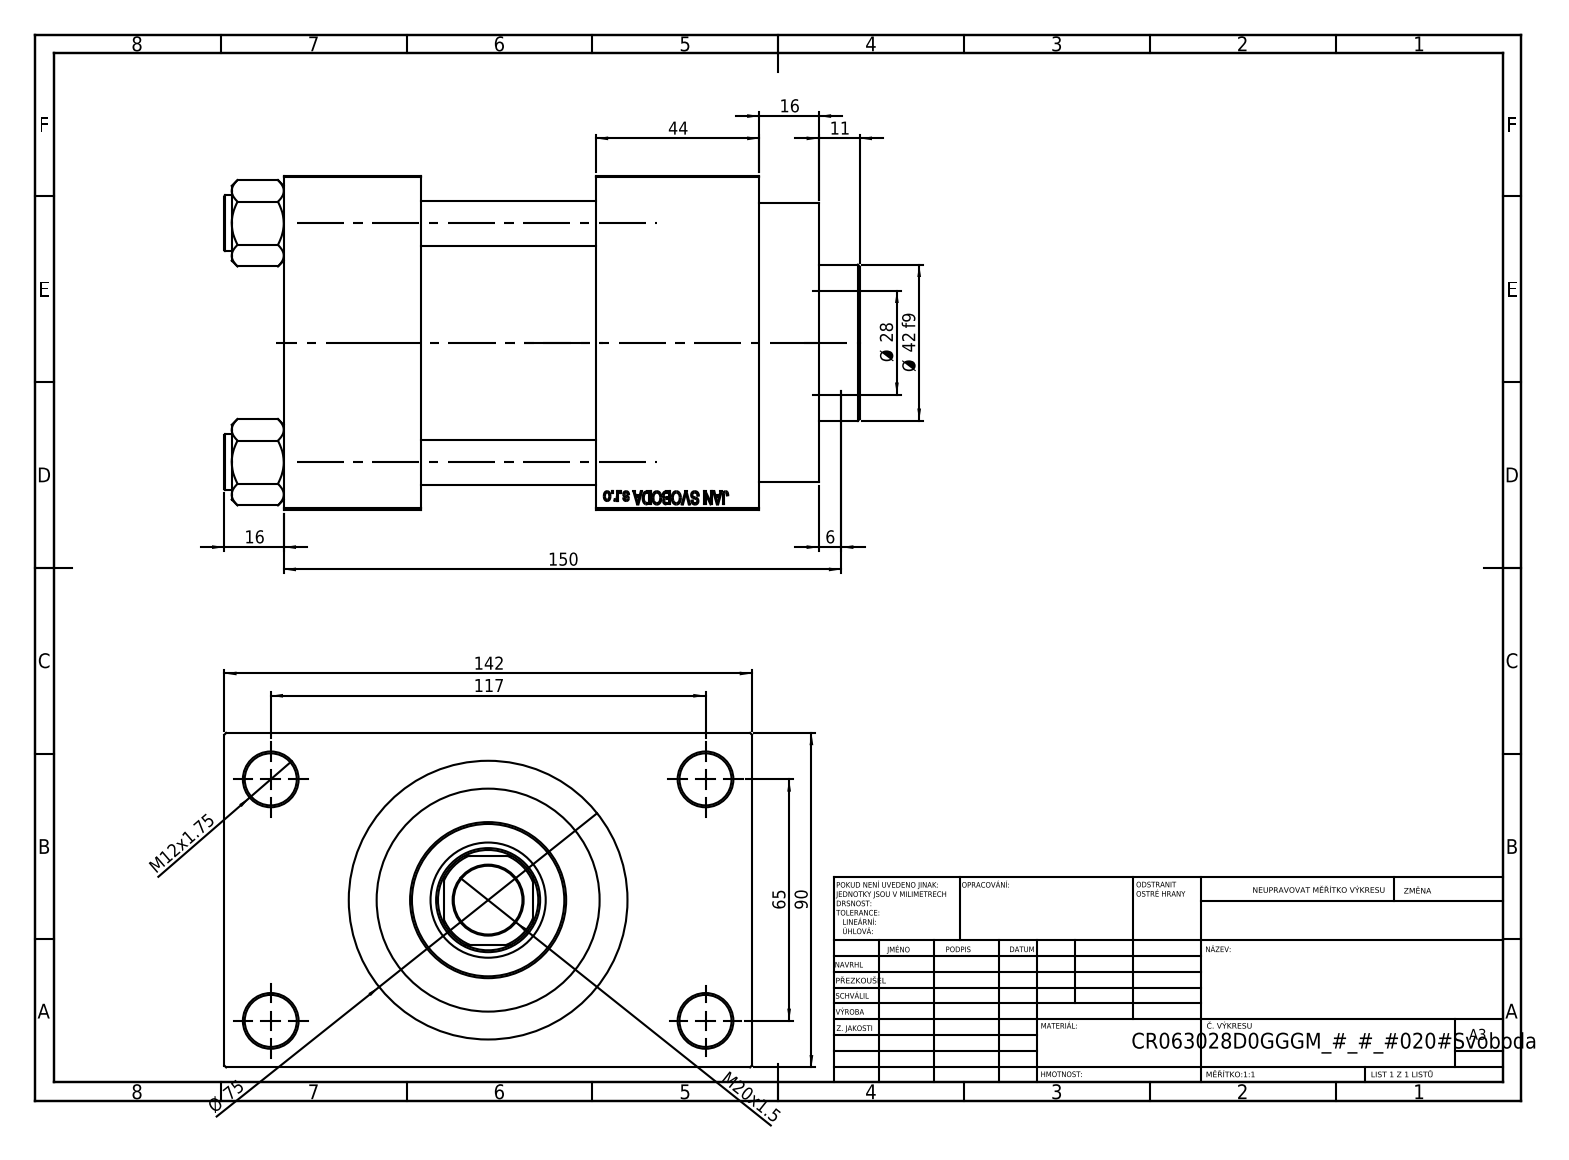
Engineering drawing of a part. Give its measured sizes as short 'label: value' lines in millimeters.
name: V215CR_VCP_D; V215CR_D_TYCINKA; V215_VC_A; NUT_M5_D (+1 more)
written by: SolidWorks 2019 (CONFIG_CONTROL_DESIGN)
unit: mm
bodies: 11 solids, 1104 faces (497 planar, 89 cylindrical, 518 other)
size: 171 × 142 × 90
volume: 1 030 000 mm³; area: 184 683 mm²
holes: 4× ⌀12, 4× ⌀14, 2× ⌀7, 2× ⌀20.96, 2× ⌀30, 1× ⌀18.5, 1× ⌀28, 1× ⌀31, 1× ⌀50, 1× ⌀60, 1× ⌀63
bosses: 4× ⌀15, 1× ⌀75, 1× ⌀69, 1× ⌀42
rounds: 1× R13.5
face distances: 90, 47, 37, 84, 91, 128, 44, 26, 116, 64
hole spacings: 26.35, 45.47, 64.3, 66.92, 69.81, 90.65, 111.34, 65
